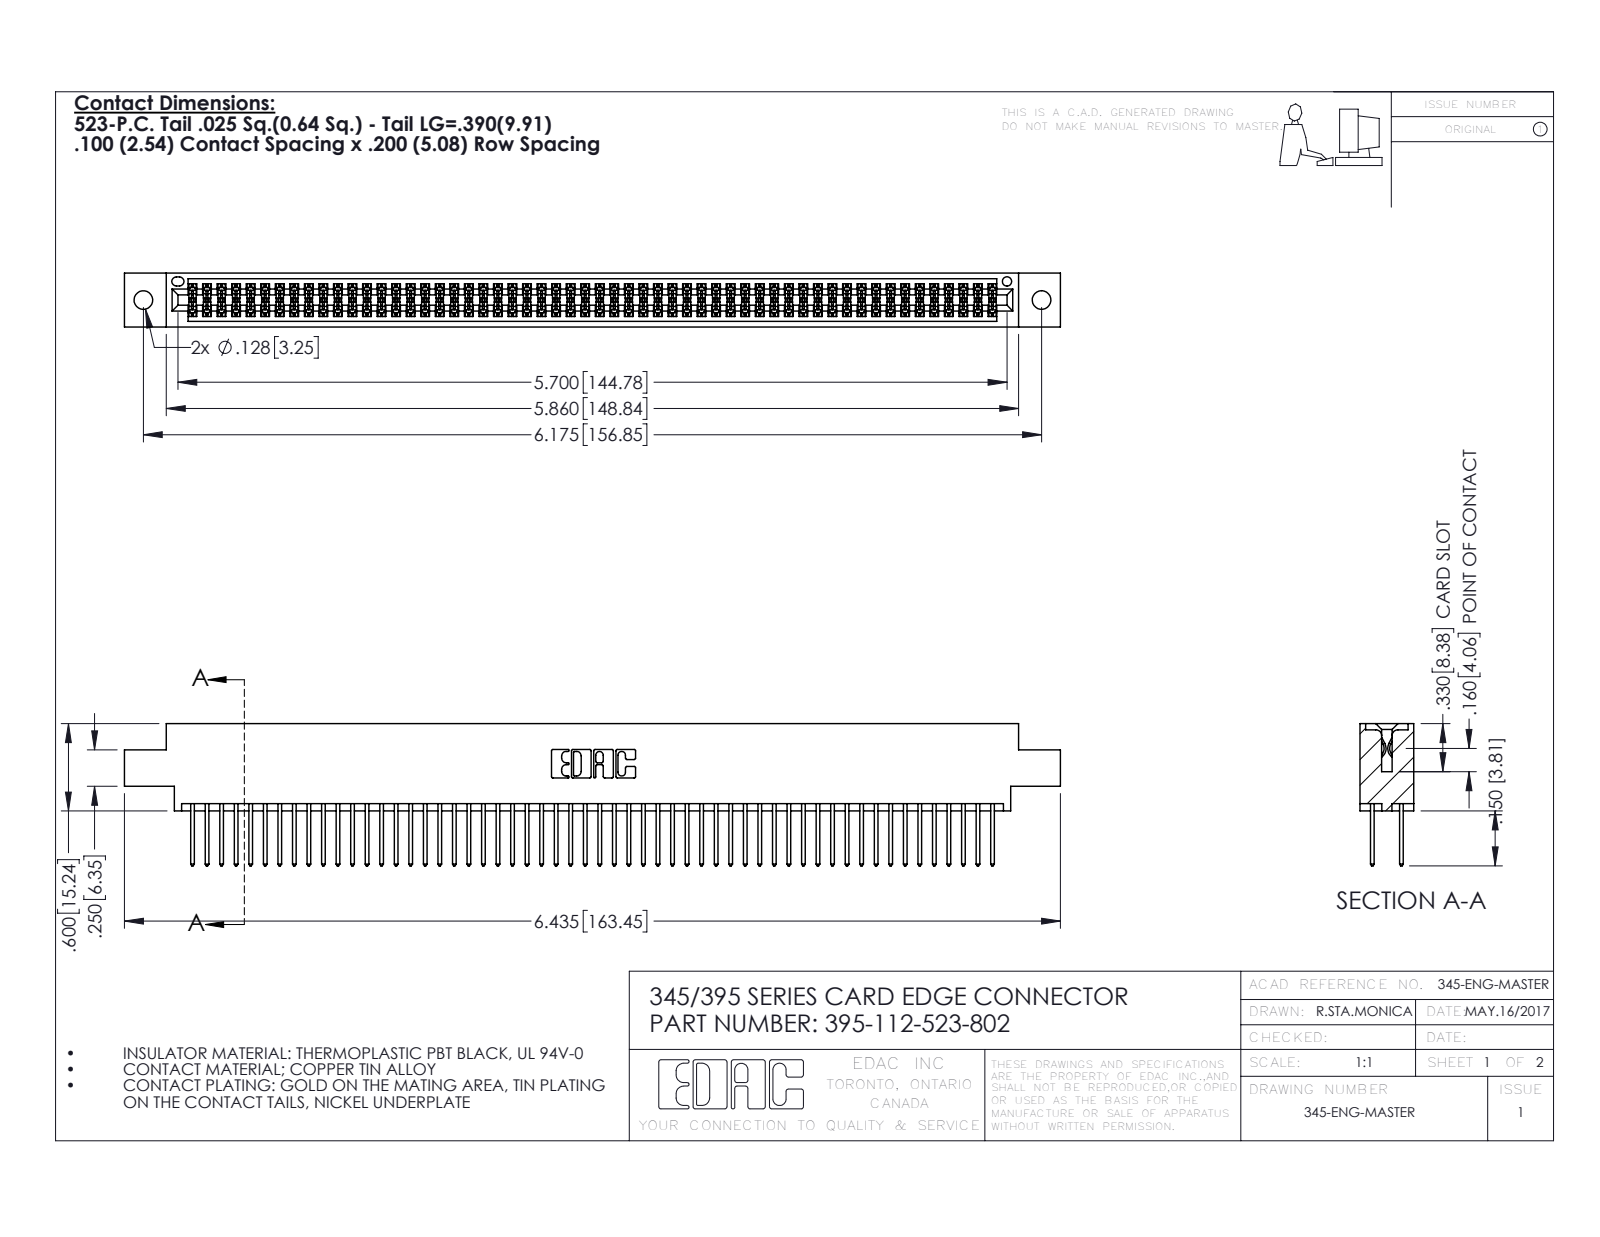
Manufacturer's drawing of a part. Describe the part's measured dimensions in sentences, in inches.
The part is named "395-112-523-802; 345-292-001_345-293-123; 345 Part_0.170 Offset - 0.128 Dia". Its 3-D file was written by "SolidWorks 2016 (CONFIG_CONTROL_DESIGN)". It is 113 solids with 5730 faces: 3780 planar, 1950 cylindrical and 0 other. Overall it measures 6.435 by 0.977 by 0.37 inches. Its volume is 0.982 cubic inches and its surface area 38.67 square inches. Round holes: 2 of diameter 0.128, 1 of diameter 0.064. Partial cylindrical surfaces (rounded edges, fillets, slot ends): 168 of radius 0.006, 112 of radius 0.01, 22 of radius 0.01, 6 of radius 0.007, 6 of radius 0.031, 3 of radius 0.026, 2 of radius 0.014, 2 of radius 0.019. The main face-to-face distances are 0.072, 0.298, 0.2, 0.098, 0.272, 0.025, 0.37, 0.225, 0.175, 0.149. The hole center spacings are 0.27, 5.939, 6.175.
